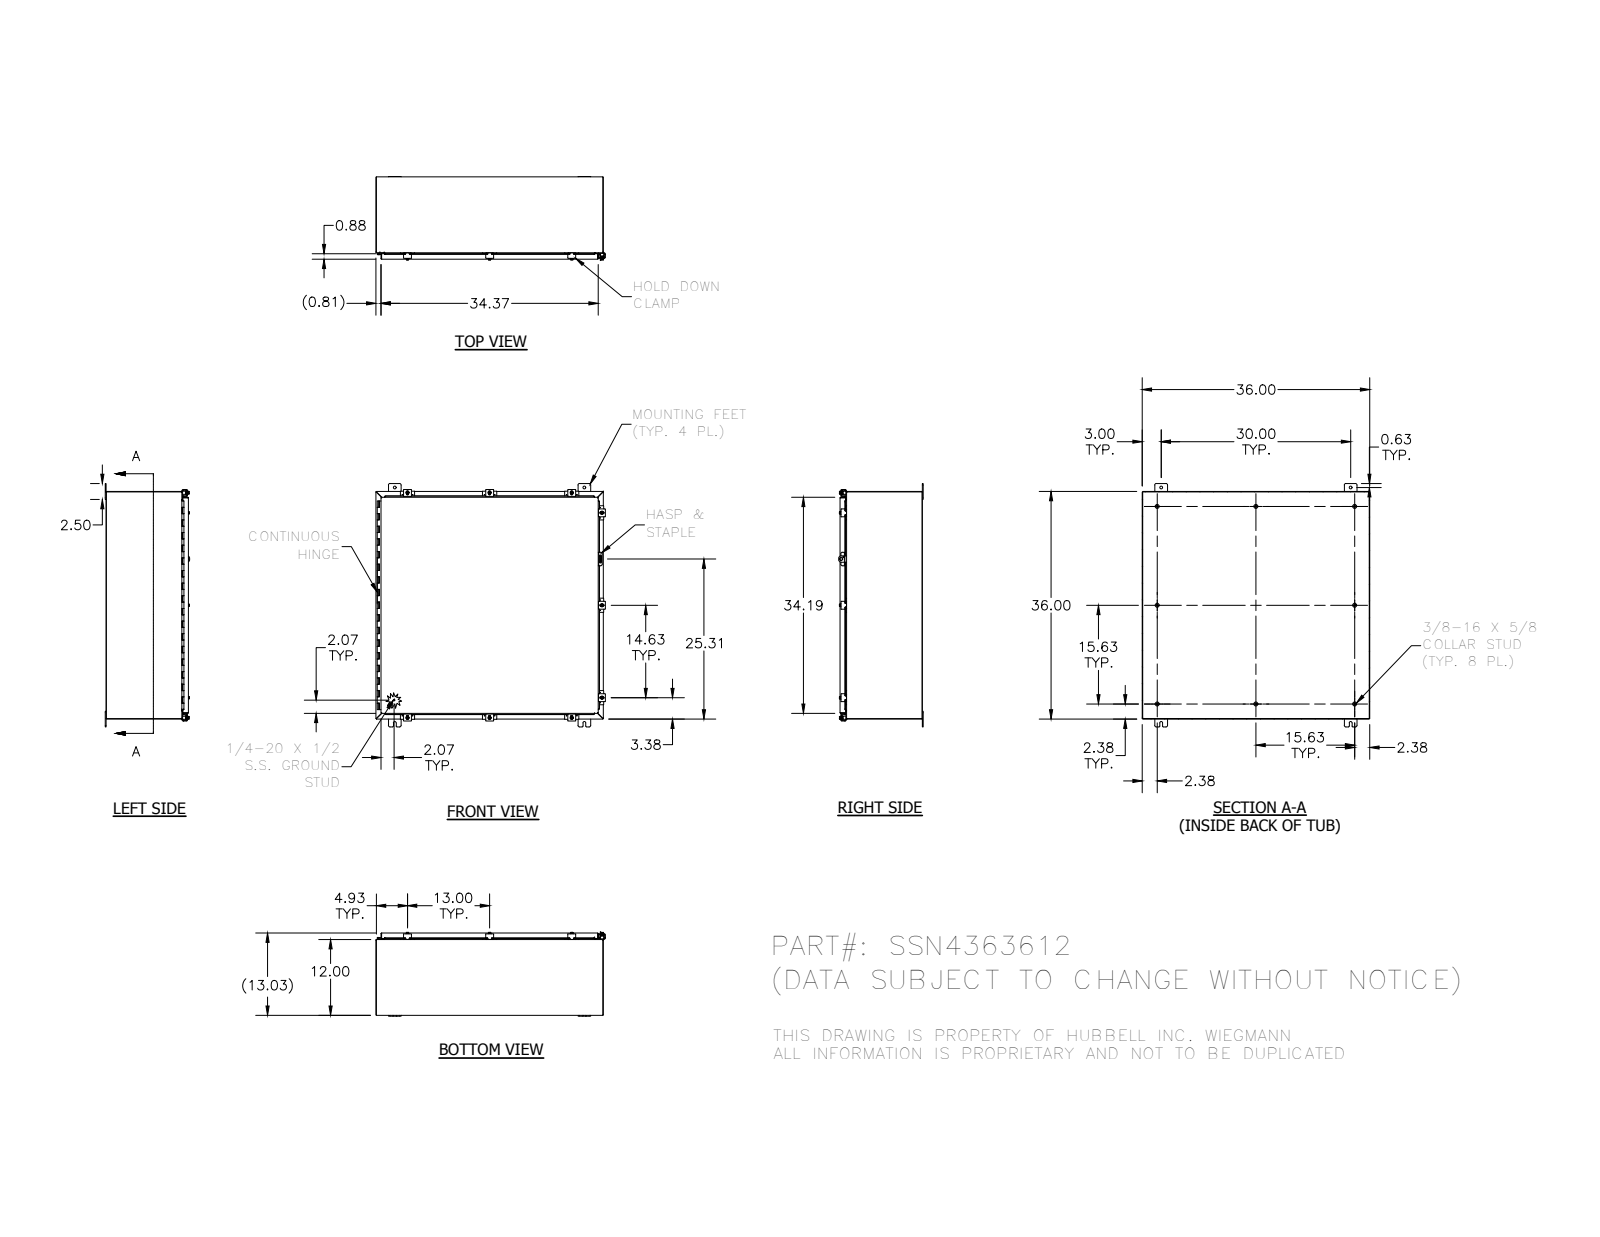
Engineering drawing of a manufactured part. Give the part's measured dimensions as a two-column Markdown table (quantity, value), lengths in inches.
| quantity | value |
| --- | --- |
| part name | 32874-36P; SSN43636LID; 30824-1; 30818 (+8 more) |
| STEP written by | SolidWorks 2014 (AUTOMOTIVE_DESIGN) |
| units | inches |
| bodies | 68 solids, 2586 faces (1006 planar, 1117 cylindrical, 463 other) |
| overall size | 38.5 × 36.311 × 13.355 |
| volume | 369 in³ |
| surface area | 9 773 in² |
| round holes (diameter × count) | 0.11 × 21, 0.211 × 9, 0.281 × 9, 0.3 × 9, 0.438 × 4, 0.125 × 1, 0.156 × 1, 0.5 × 1 |
| round bosses / shafts (diameter × count) | 0.25 × 11, 0.52 × 9, 0.5 × 9, 0.35 × 9, 0.625 × 8, 0.33 × 8, 0.337 × 1, 0.12 × 1 |
| partial cylindrical surfaces (radius × count) | 0.03 × 105, 0.125 × 39, 0.25 × 35, 0.031 × 21, 0.105 × 21, 0.141 × 18, 0.062 × 16, 0.1 × 12 |
| main face-to-face distances | 0.074, 12.959, 35.926, 12.885, 13.033, 35.852, 36, 11.926, 1.033, 12 |
| hole center spacings | 0.876, 13, 35.298, 13.817, 12.192, 37.299, 37.334, 37.896 |
